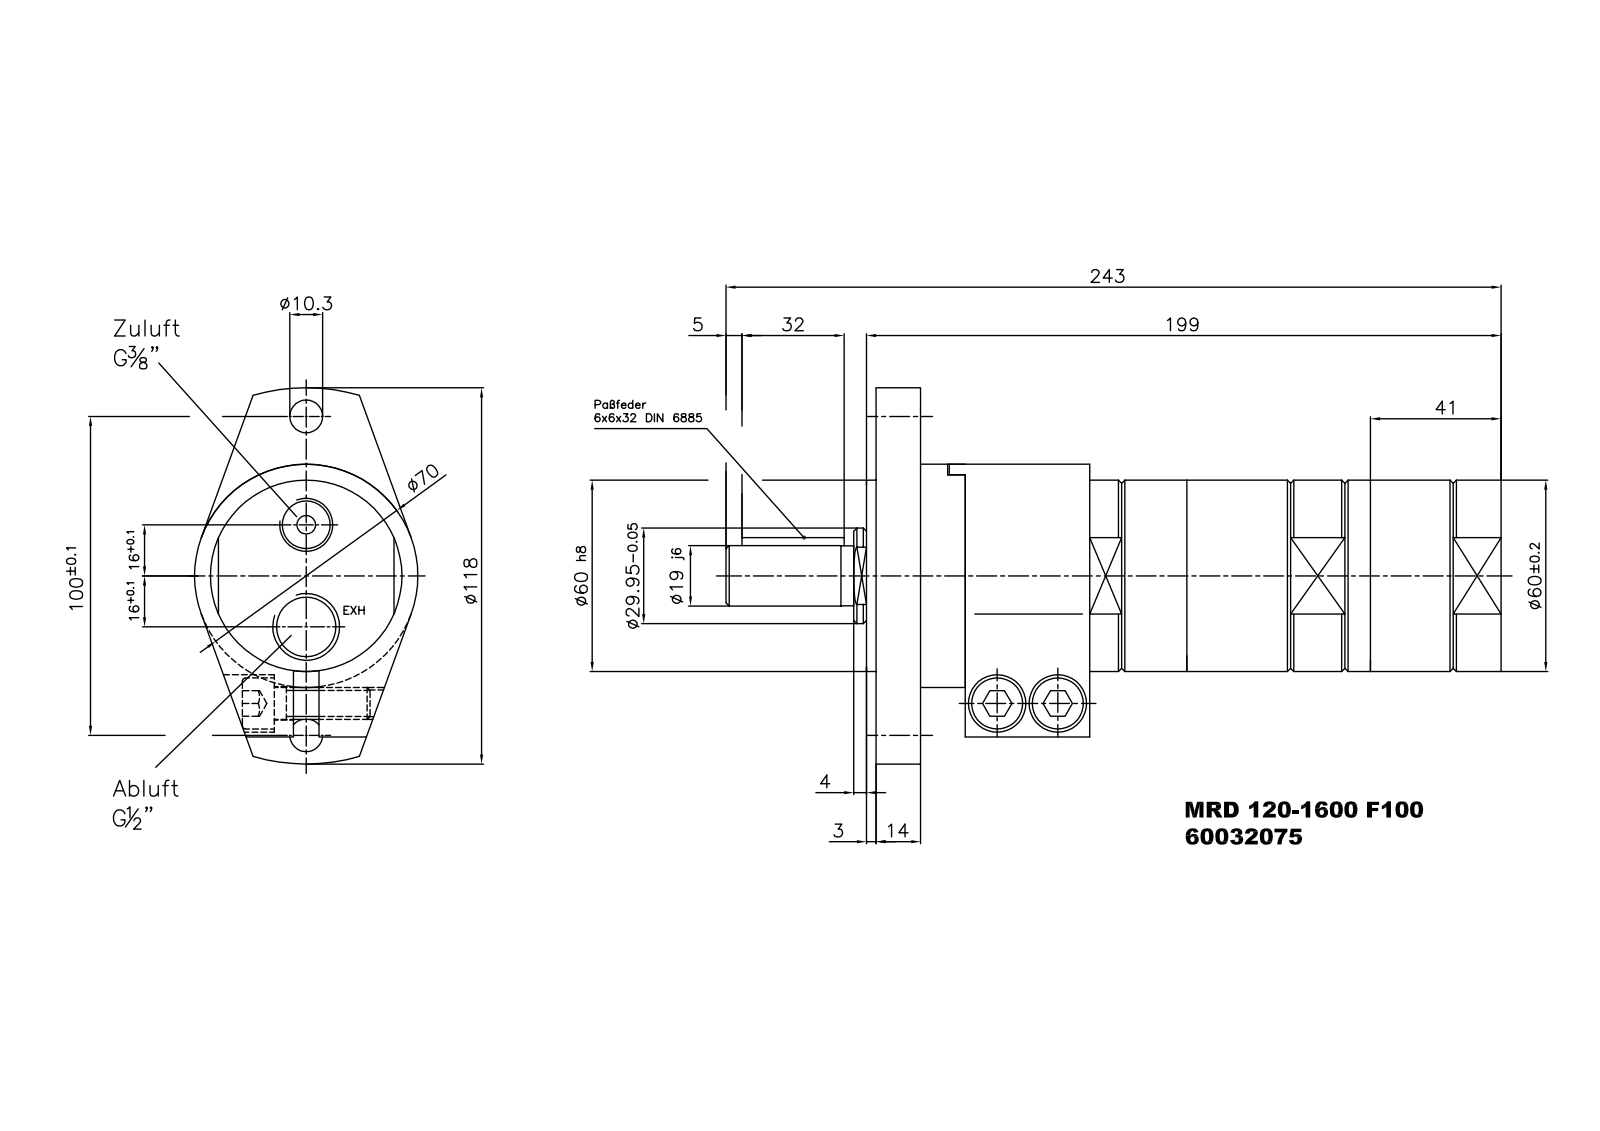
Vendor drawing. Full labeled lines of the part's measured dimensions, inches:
Part name (STEP PRODUCT): MRD 120-9300 F100_60032095
STEP written by: Autodesk Inventor 2014 (AUTOMOTIVE_DESIGN)
Units: inches
Bodies: 1 solid, 156 faces (85 planar, 36 cylindrical, 35 other)
Overall size (bounding box): 9.567 × 4.646 × 2.756
Volume: 38.08 in³ · Surface area: 90.06 in²
Round holes (diameter × count): ⌀0.406 ×2, ⌀0.061 ×1, ⌀0.063 ×1, ⌀0.157 ×1, ⌀0.217 ×1, ⌀0.589 ×1, ⌀0.733 ×1, ⌀1.378 ×1
Round bosses / shafts (diameter × count): ⌀2.756 ×1, ⌀2.362 ×1, ⌀1.179 ×1, ⌀0.748 ×1, ⌀0.74 ×1, ⌀0.197 ×1, ⌀0.142 ×1, ⌀0.13 ×1
Partial cylindrical surfaces — rounded edges, fillets, slot ends (radius × count): R0.118 ×2, R2.323 ×1
Main face-to-face distances: 0.551, 7.717, 7.165, 0.118, 0.669, 7.835, 2.165, 1.22, 1.102, 6.614
Hole centre spacings: 0.63, 1.339, 1.969, 2.598, 1.26, 3.937
